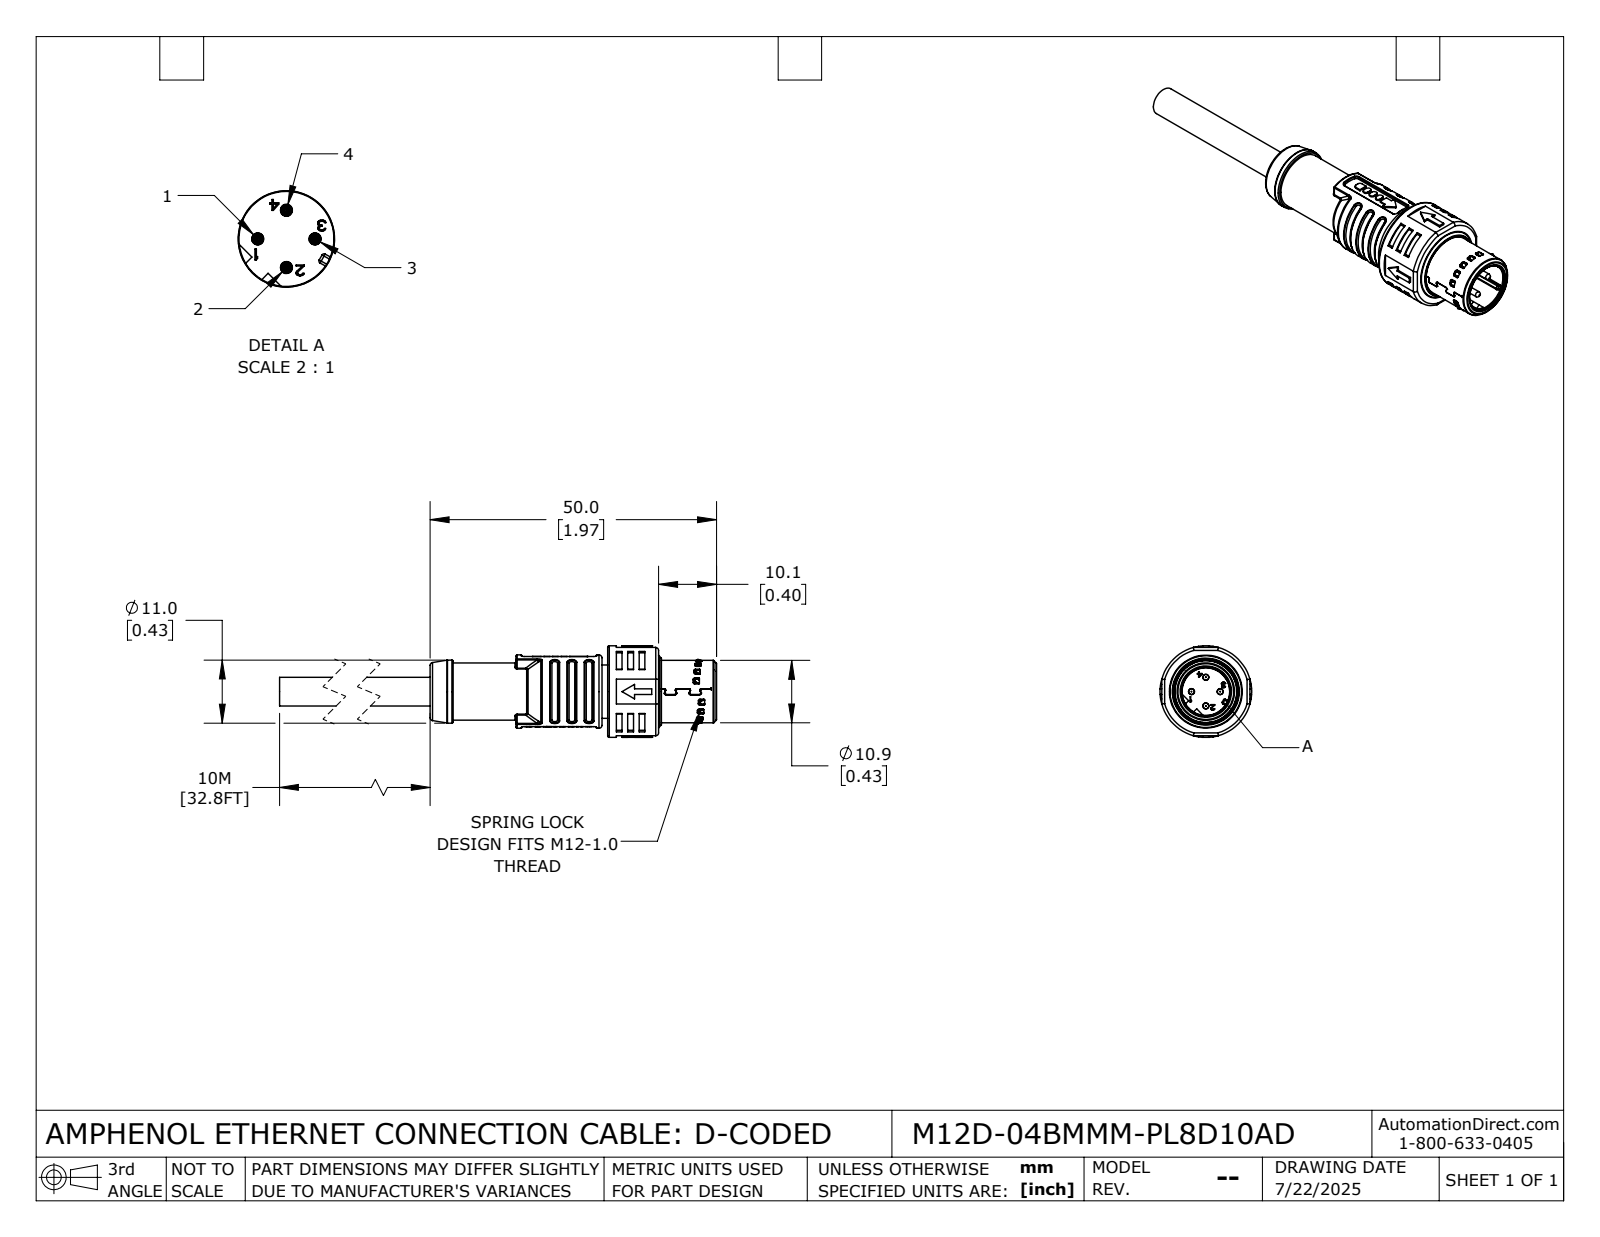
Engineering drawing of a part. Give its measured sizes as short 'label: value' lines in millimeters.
name: M12D-04BMMM-PL8D10AD
written by: SolidWorks 2024 (CONFIG_CONTROL_DESIGN)
unit: mm
bodies: 1 solid, 2139 faces (996 planar, 644 cylindrical, 499 other)
size: 80 × 16 × 16
volume: 5 399 mm³; area: 5 961 mm²
holes: 4× ⌀1.05, 1× ⌀8.3, 1× ⌀9, 1× ⌀10.15, 1× ⌀10.5, 1× ⌀10.9, 1× ⌀11.5, 1× ⌀11.8, 1× ⌀14.2
bosses: 4× ⌀1, 1× ⌀16, 1× ⌀14.1, 1× ⌀12.8, 1× ⌀12.4, 1× ⌀11, 1× ⌀10.45, 1× ⌀10.4
rounds: 119× R0.2, 66× R0.25, 64× R0.3, 44× R0.15, 38× R0.5, 12× R0.13, 11× R0.7, 7× R0.1
face distances: 1, 30, 10.1, 8.9, 2.5, 1.2, 8.6, 32.5, 15.4, 1.5
hole spacings: 2.5, 3.54, 5
